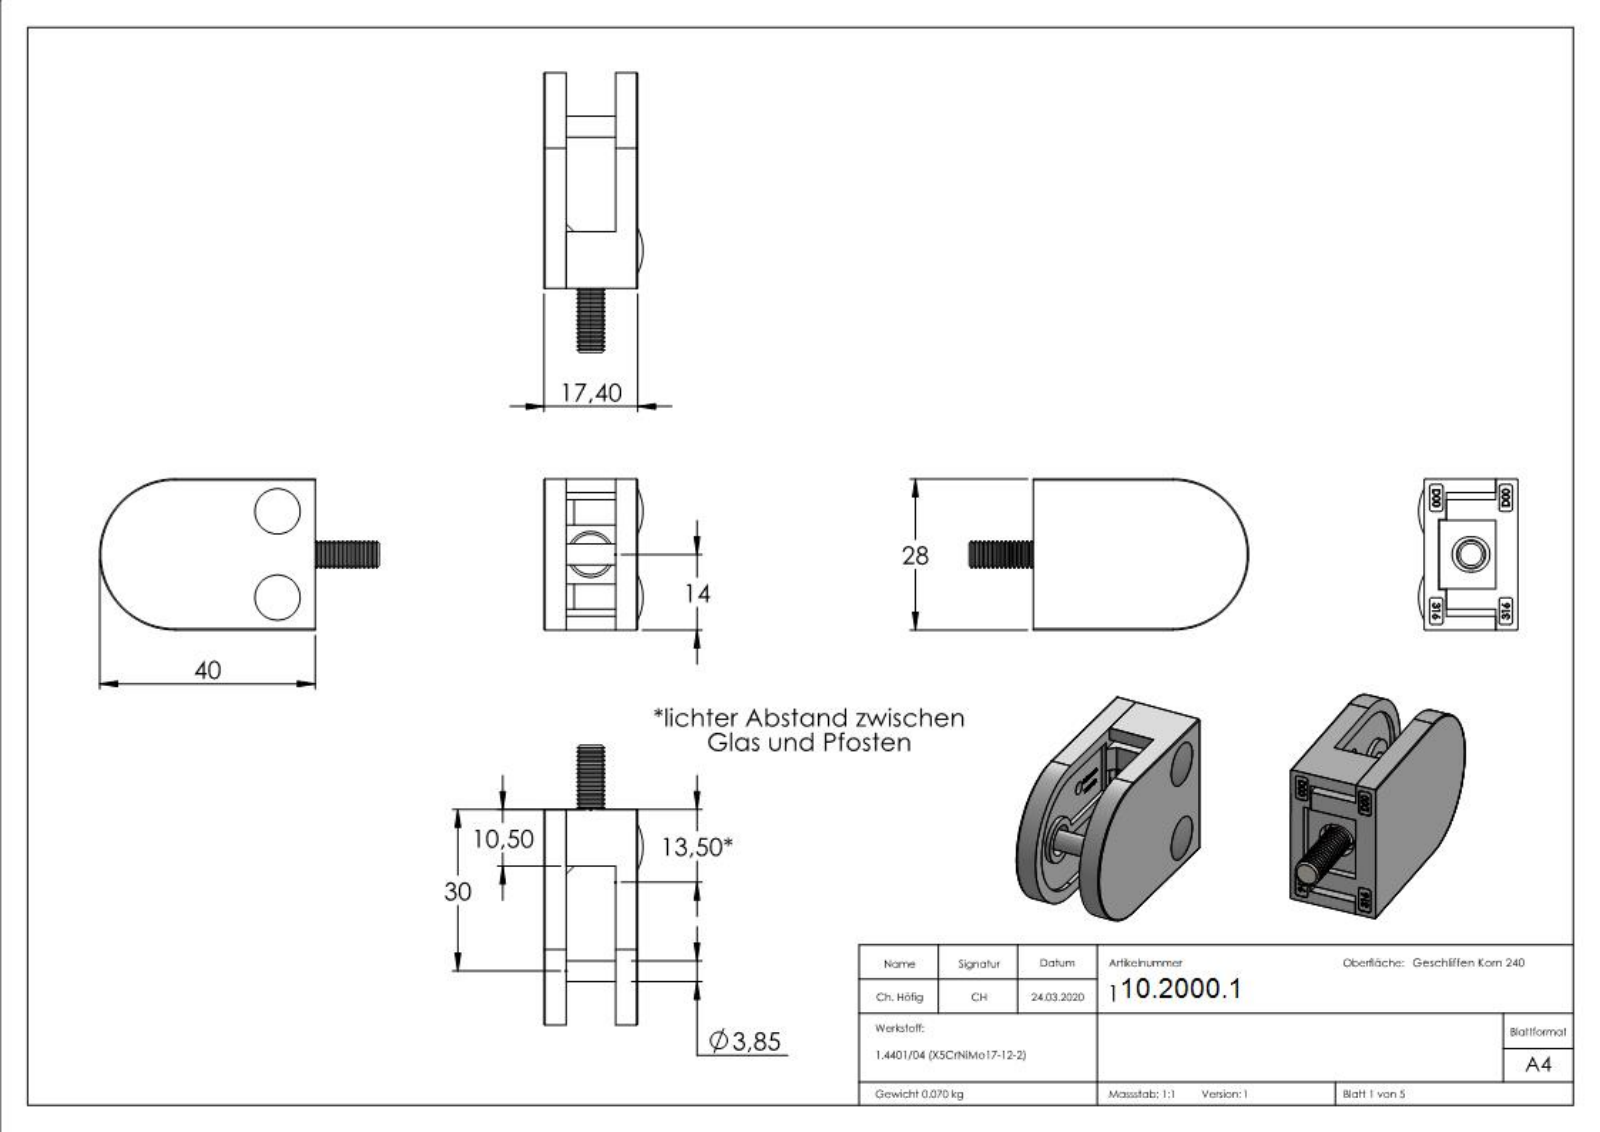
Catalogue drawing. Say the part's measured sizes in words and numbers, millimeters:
The part is named "1600-V4A; socket countersunk head screw_din_DIN 7991 - M4 x 10 --- 10S; 16-Stift_16-Stift; 16xx-XXX Teil1_1600-V4A (+3 more)". Its 3-D file was written by "SolidWorks 2015 (CONFIG_CONTROL_DESIGN)". It is 8 solids with 1187 faces: 543 planar, 160 cylindrical and 484 other. Overall it measures 51.9 by 28 by 18.4 millimeters. Its volume is 9 512 cubic millimeters and its surface area 8 729 square millimeters. Round holes: 2 of diameter 1, 2 of diameter 2.5, 2 of diameter 3.3, 2 of diameter 4.15, 2 of diameter 8.2, 1 of diameter 3.9, 1 of diameter 6. Round bosses or shafts: 2 of diameter 7.64, 2 of diameter 4, 2 of diameter 2.5, 1 of diameter 8.8, 1 of diameter 8.5, 1 of diameter 5, 1 of diameter 3.85. Partial cylindrical surfaces (rounded edges, fillets, slot ends): 20 of radius 0.5, 4 of radius 0.2, 2 of radius 3.25, 1 of radius 11.6, 1 of radius 14. The main face-to-face distances are 17.4, 4.1, 3.2, 14.2, 13.3, 0.9, 10.1, 11, 9.2, 2.5. The hole center spacings are 10.99, 14.1, 20.01, 24.35, 12.6, 16.
